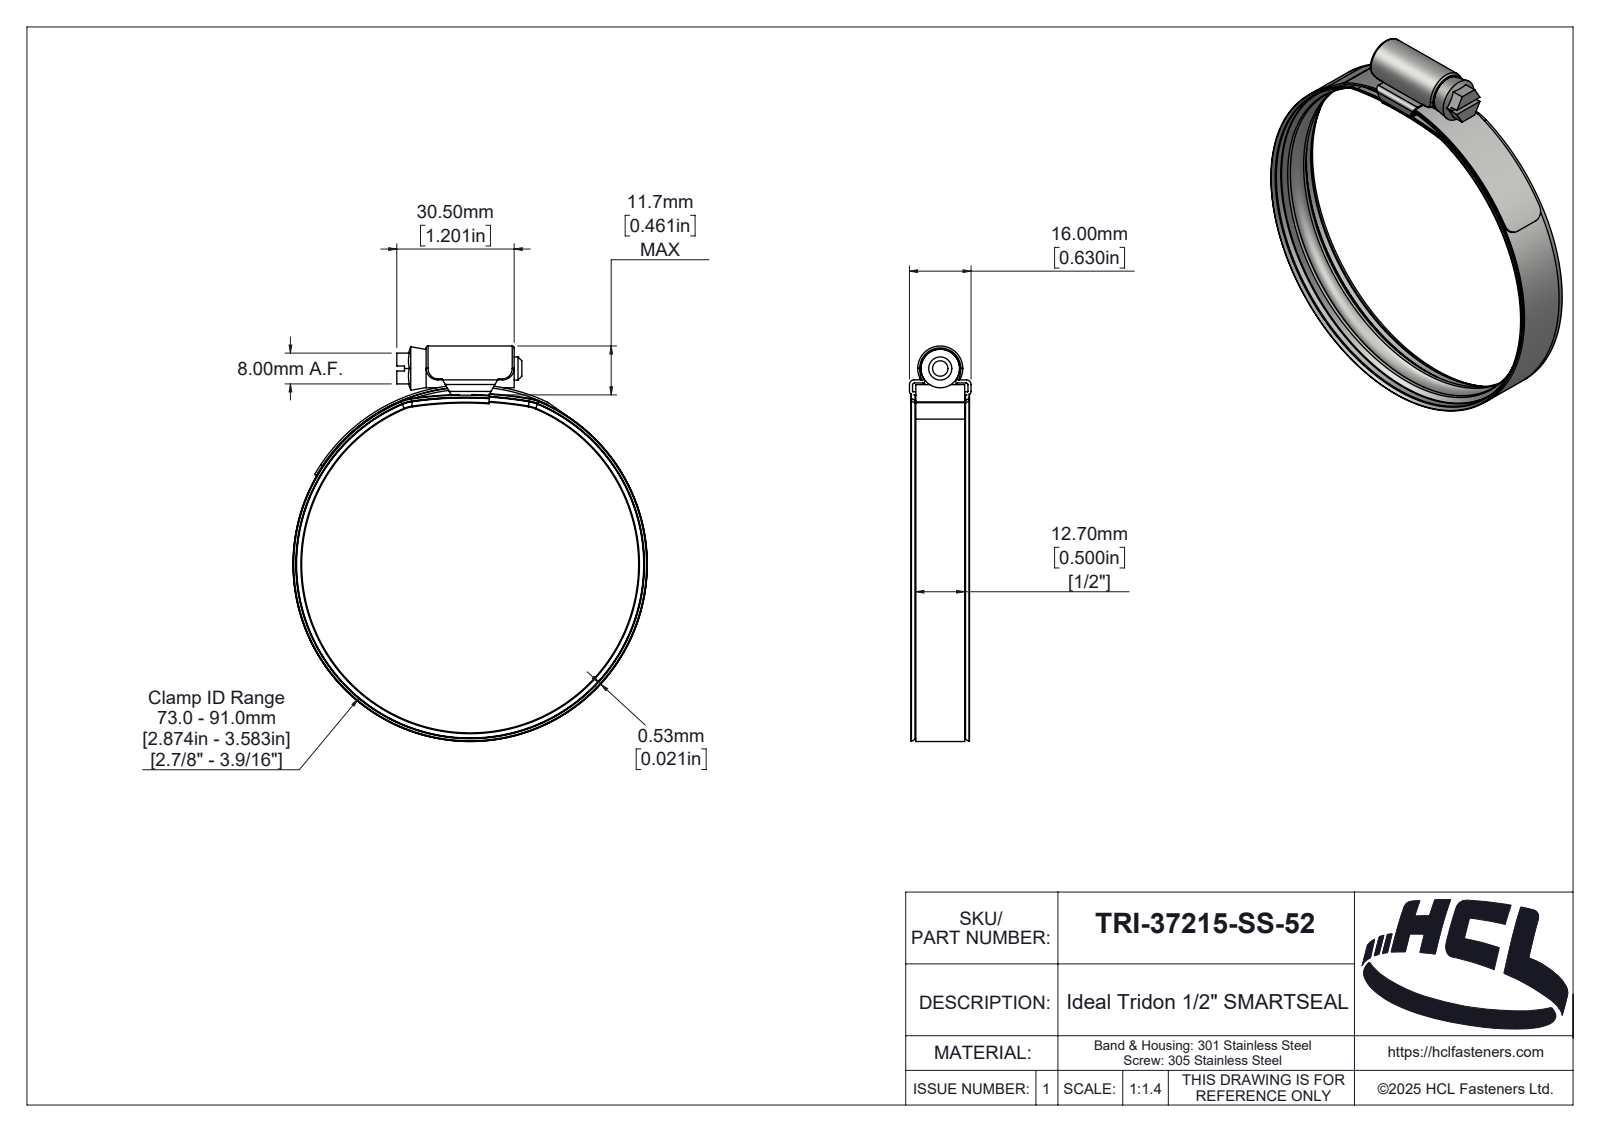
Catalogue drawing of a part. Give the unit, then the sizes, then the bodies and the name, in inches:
Units: inches
Overall size (bounding box): 4.044 × 3.624 × 0.63
Round holes (diameter × count): ⌀3.559 ×1, ⌀3.583 ×1
Round bosses / shafts (diameter × count): ⌀3.624 ×1, ⌀3.575 ×1, ⌀0.394 ×1, ⌀0.236 ×1
Partial cylindrical surfaces — rounded edges, fillets, slot ends (radius × count): R0.02 ×6, R0.118 ×4, R0.004 ×2, R0.035 ×2, R0.047 ×2, R0.39 ×2, R0.398 ×2, R0.018 ×1
Main face-to-face distances: 0.031, 0.5, 0.122, 0.021, 0.091, 1.201, 0.154, 0.065, 0.565, 0.598
Volume: 0.385 in³ · Surface area: 33.88 in²
Bodies: 4 solids, 418 faces (42 planar, 119 cylindrical, 257 other)
Part name (STEP PRODUCT): TRI-37215-SS-52
STEP written by: SolidWorks 2025 (AUTOMOTIVE_DESIGN)
